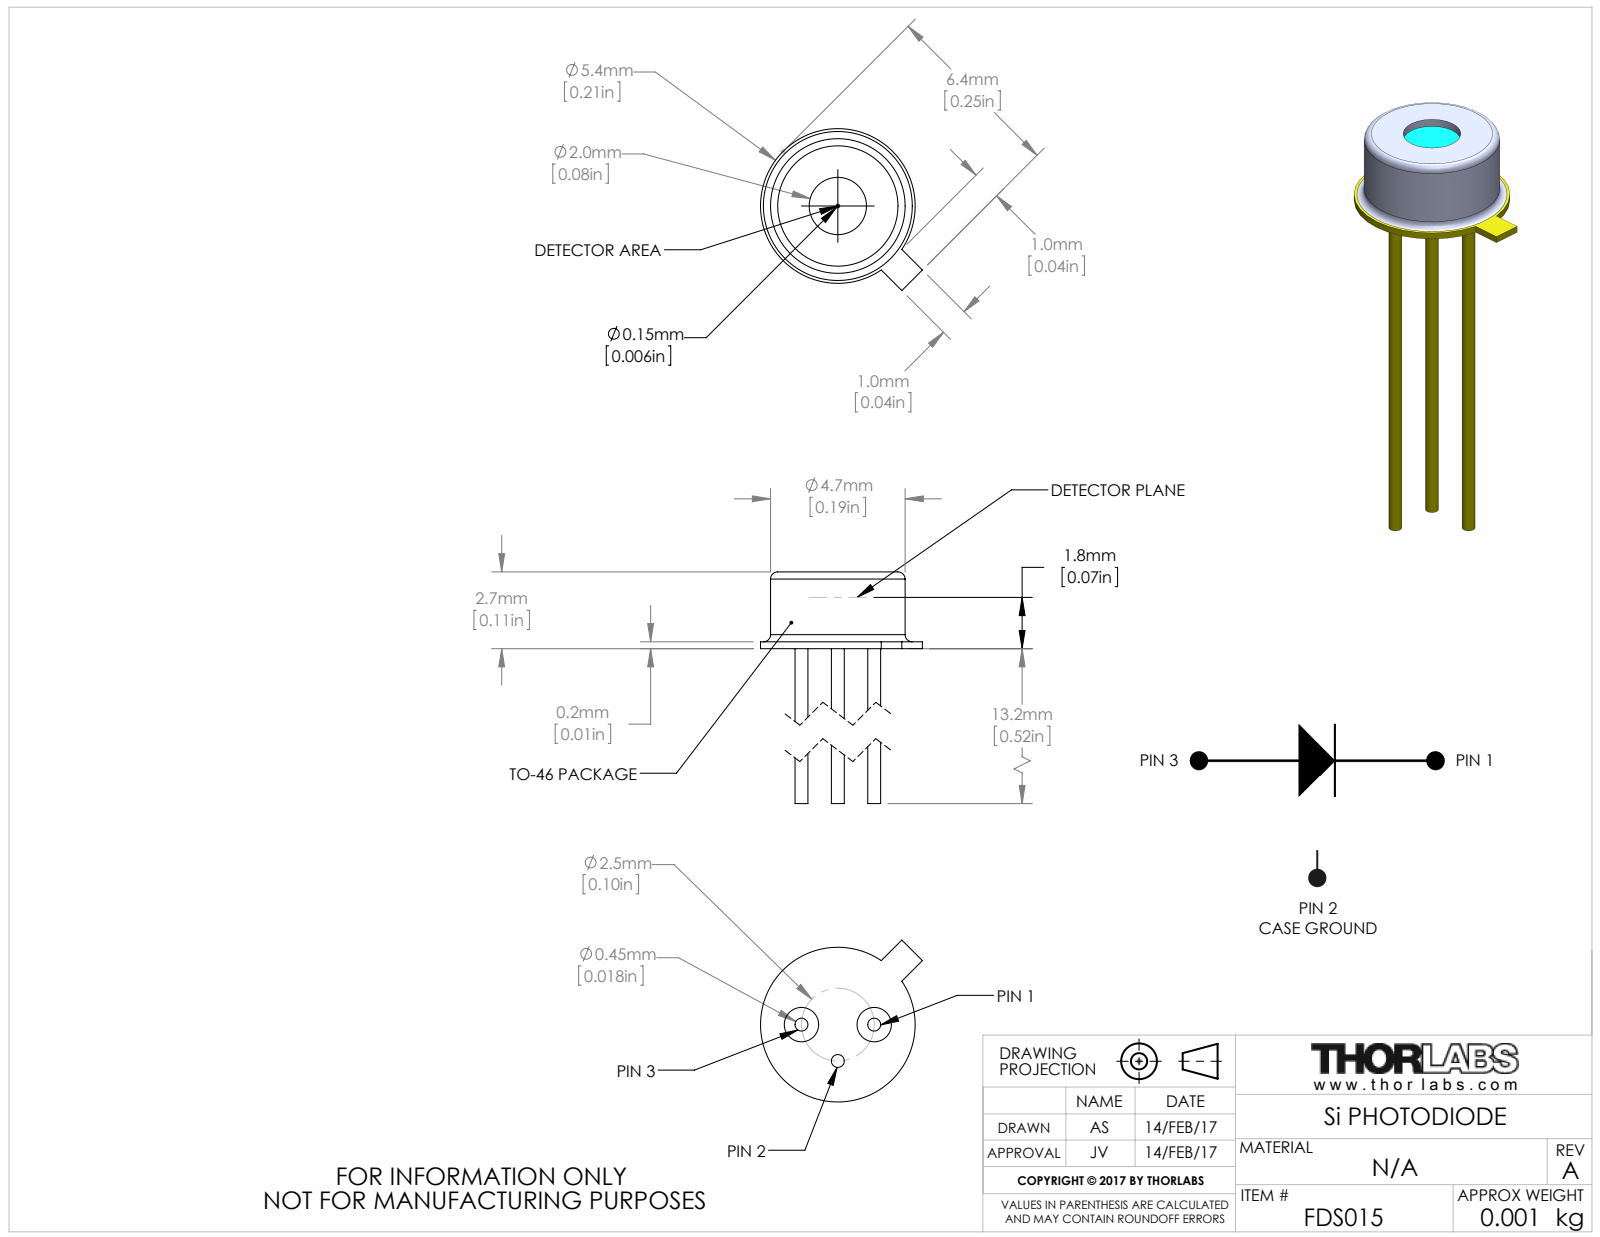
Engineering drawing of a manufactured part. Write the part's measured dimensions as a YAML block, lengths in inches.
part_name: "FDS015"
step_written_by: "SolidWorks 2014 (AUTOMOTIVE_DESIGN)"
units: inches
bodies: {solids: 1, faces: 29, planar: 12, cylindrical: 13, other: 4}
overall_size: [0.625, 0.222, 0.222]
volume: 0.003
surface_area: 0.222
round_holes:
  - {diameter: 0.079, count: 1}
round_bosses_or_shafts:
  - {diameter: 0.018, count: 3}
  - {diameter: 0.213, count: 1}
  - {diameter: 0.185, count: 1}
face_to_face_distances: [0.106, 0.094, 0.085, 0.096, 0.52, 0.529, 0.614, 0.625, 0.04]
